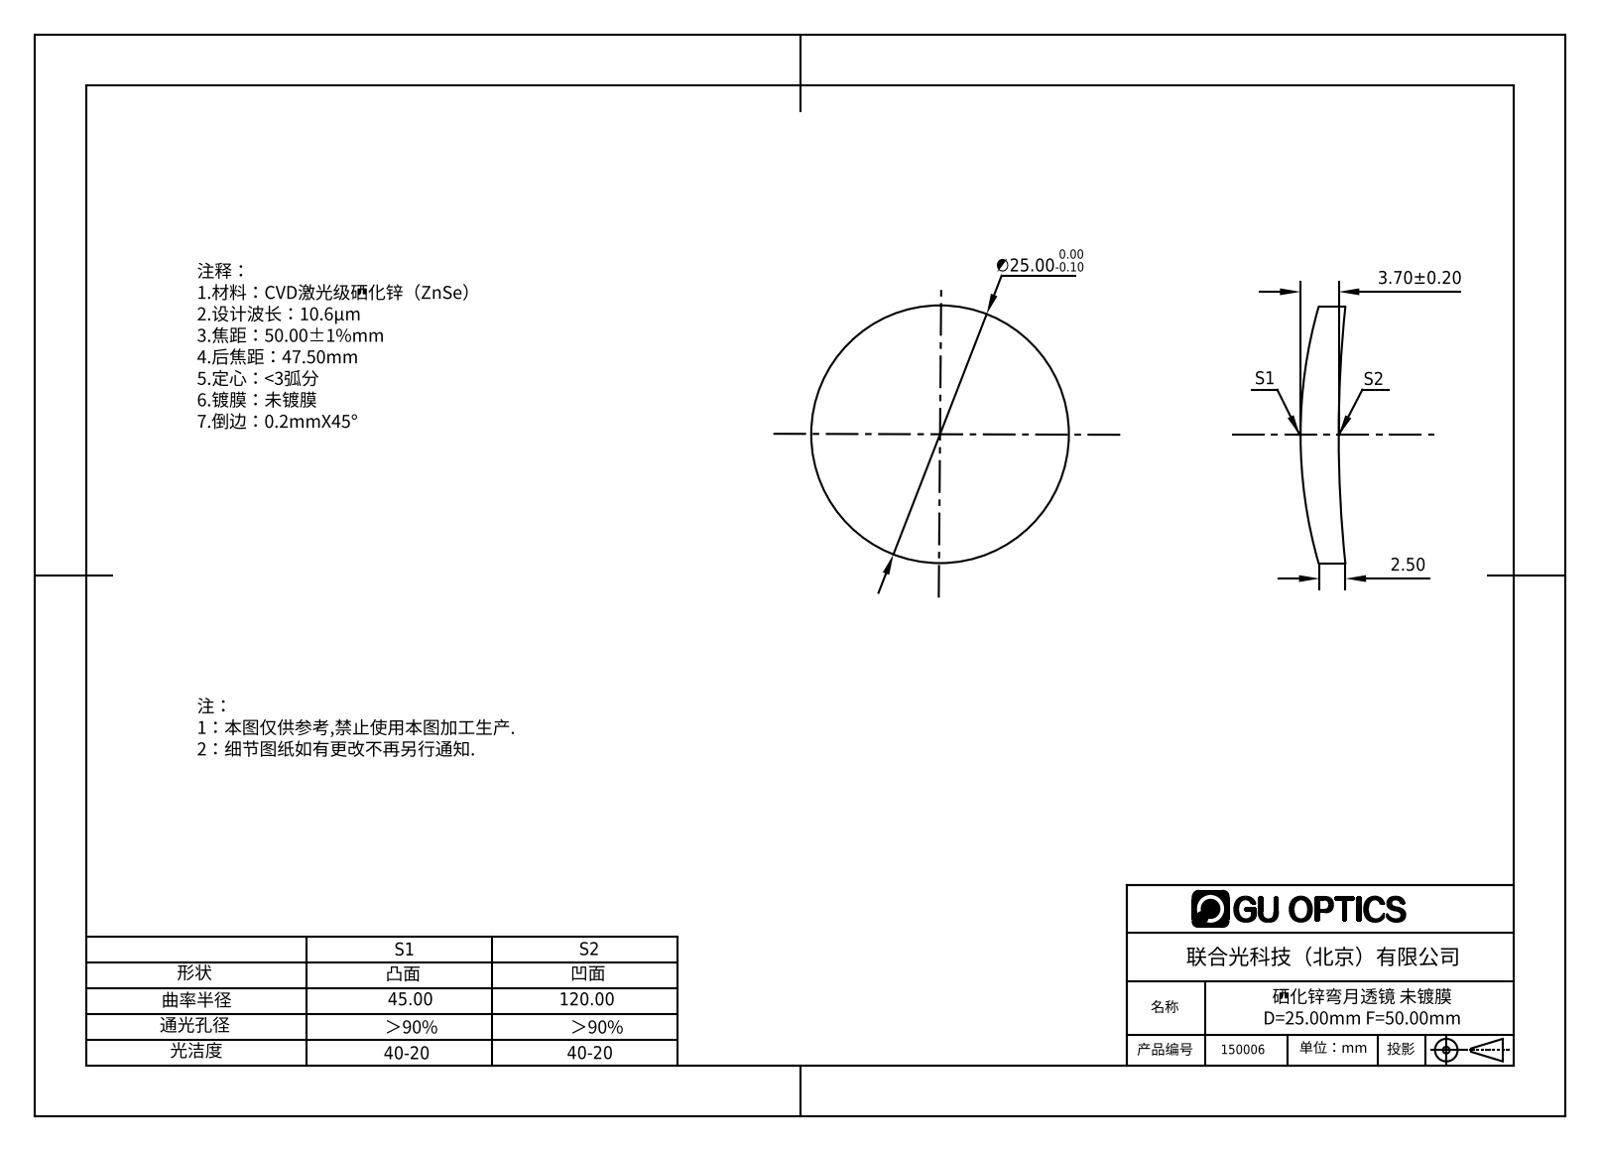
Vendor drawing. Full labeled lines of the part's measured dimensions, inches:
Part name (STEP PRODUCT): 150006
STEP written by: SolidWorks 2016 (AUTOMOTIVE_DESIGN)
Units: inches
Bodies: 1 solid, 6 faces (0 planar, 2 cylindrical, 4 other)
Overall size (bounding box): 0.984 × 0.984 × 0.171
Volume: 0.094 in³ · Surface area: 1.854 in²
Round bosses / shafts (diameter × count): ⌀0.984 ×1
